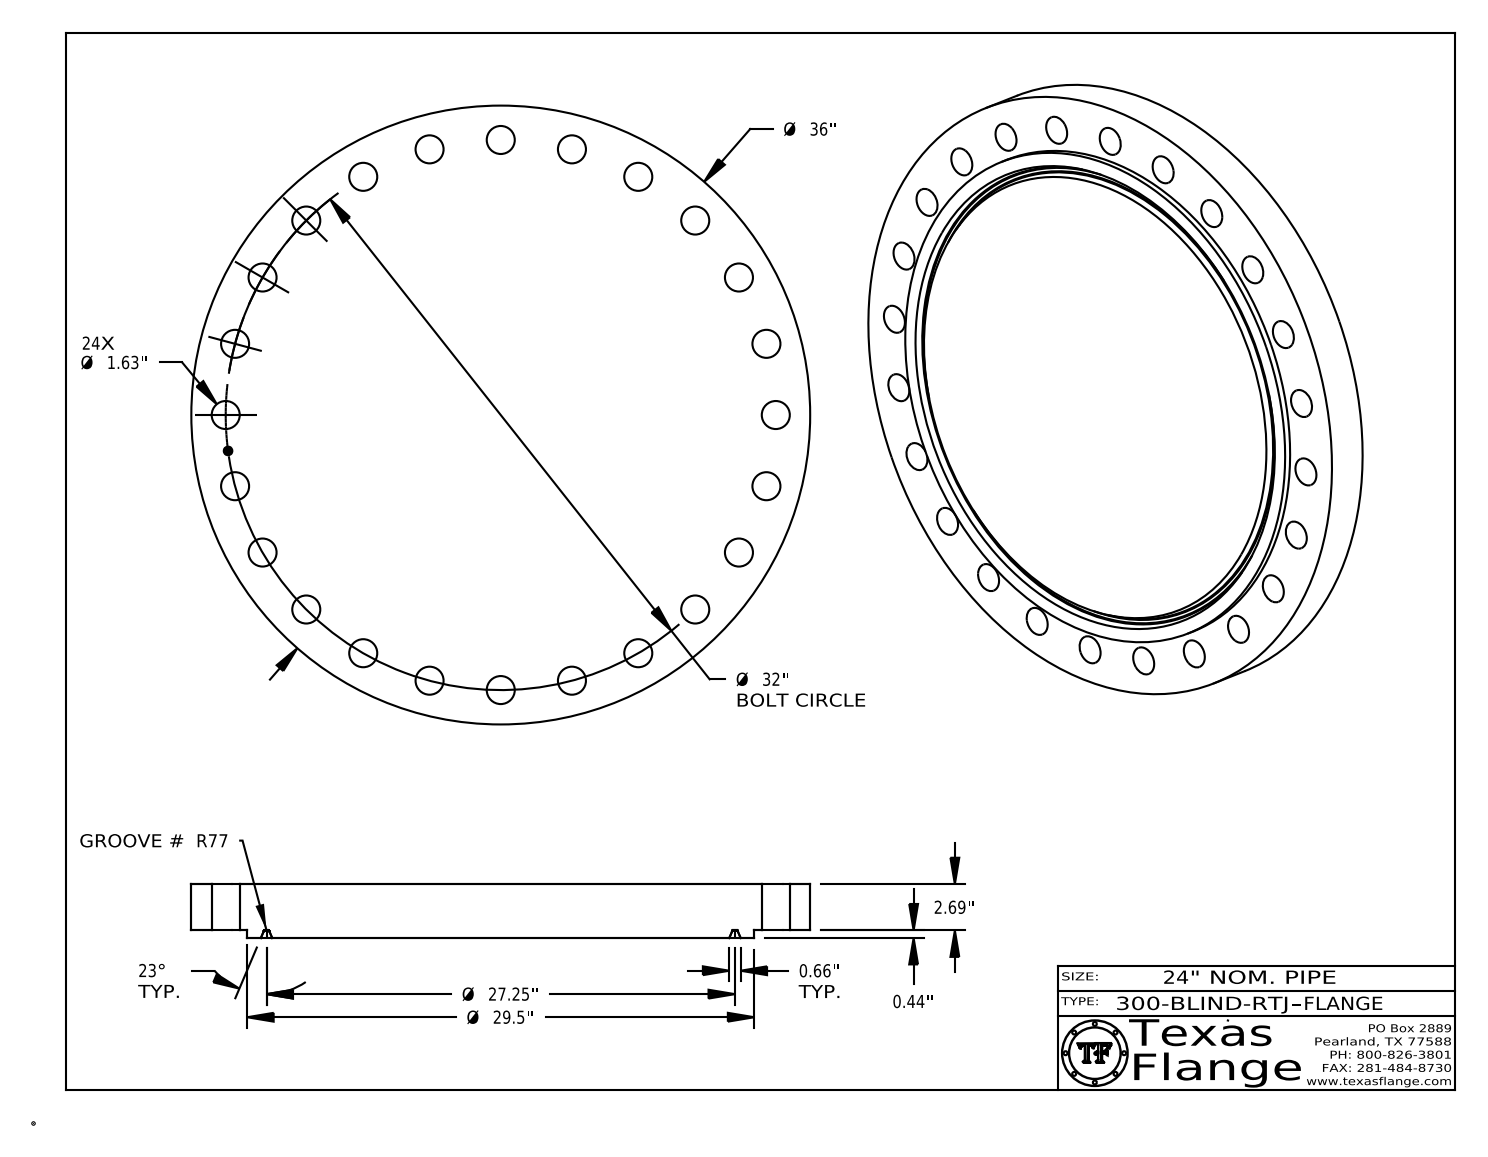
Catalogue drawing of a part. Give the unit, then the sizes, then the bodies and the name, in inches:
Units: inches
Overall size (bounding box): 36 × 36 × 3.128
Round holes (diameter × count): ⌀1.63 ×24, ⌀0.495 ×1
Round bosses / shafts (diameter × count): ⌀0.03 ×8, ⌀36 ×1, ⌀29.5 ×1, ⌀0.39 ×1
Main face-to-face distances: 3.128, 0.437, 2.69, 3.113, 2.675, 0.015, 0.147, 0.144, 0.027, 0.096
Hole centre spacings: 16, 30.909, 4.177, 8.282, 12.246, 19.48, 22.627, 25.387
Volume: 2 885 in³ · Surface area: 2 659 in²
Bodies: 1 solid, 450 faces (370 planar, 72 cylindrical, 8 other)
Part name (STEP PRODUCT): 300-BLIND-RTJ
STEP written by: CATIA V5 STEP AP214 (AUTOMOTIVE_DESIGN)
